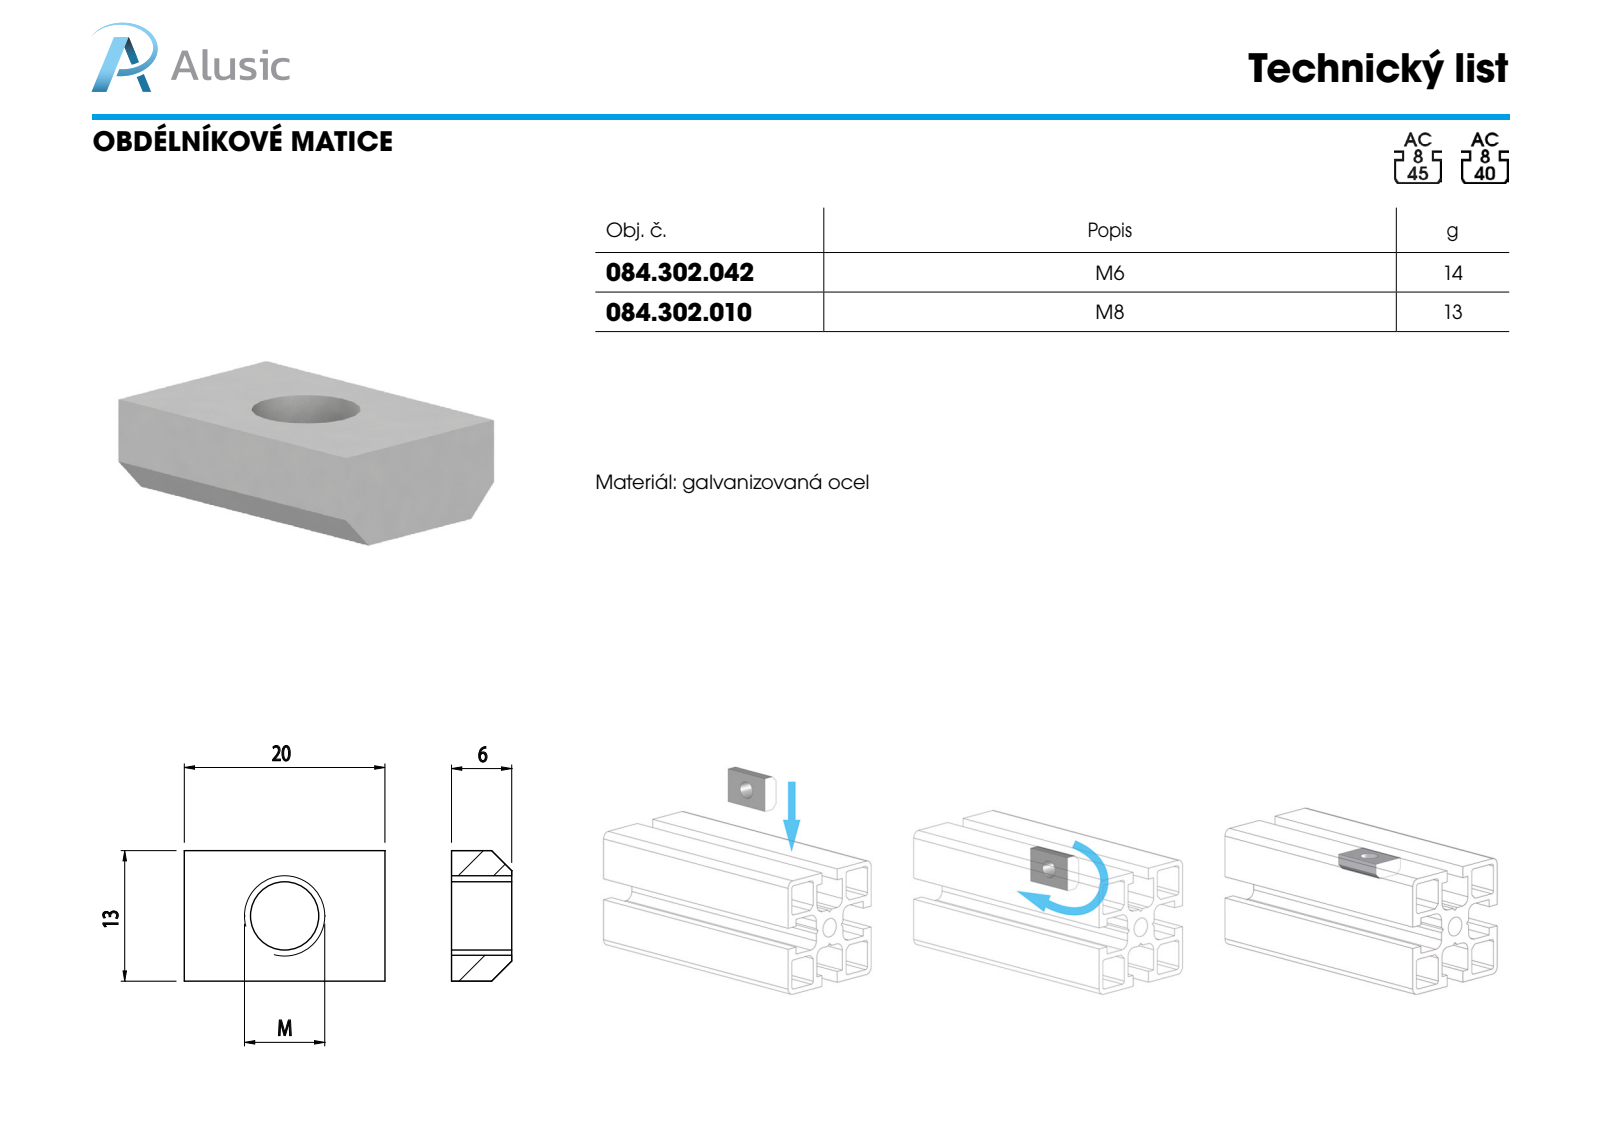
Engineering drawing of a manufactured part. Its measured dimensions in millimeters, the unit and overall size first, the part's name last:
Units: millimetres
Overall size (bounding box): 20 × 13 × 6
Round holes (diameter × count): ⌀5 ×1
Main face-to-face distances: 6, 13, 20
Volume: 1 362 mm³ · Surface area: 916 mm²
Bodies: 1 solid, 10 faces (8 planar, 2 cylindrical, 0 other)
Part name (STEP PRODUCT): 084.302.042
STEP written by: SolidWorks 2011 (CONFIG_CONTROL_DESIGN)
